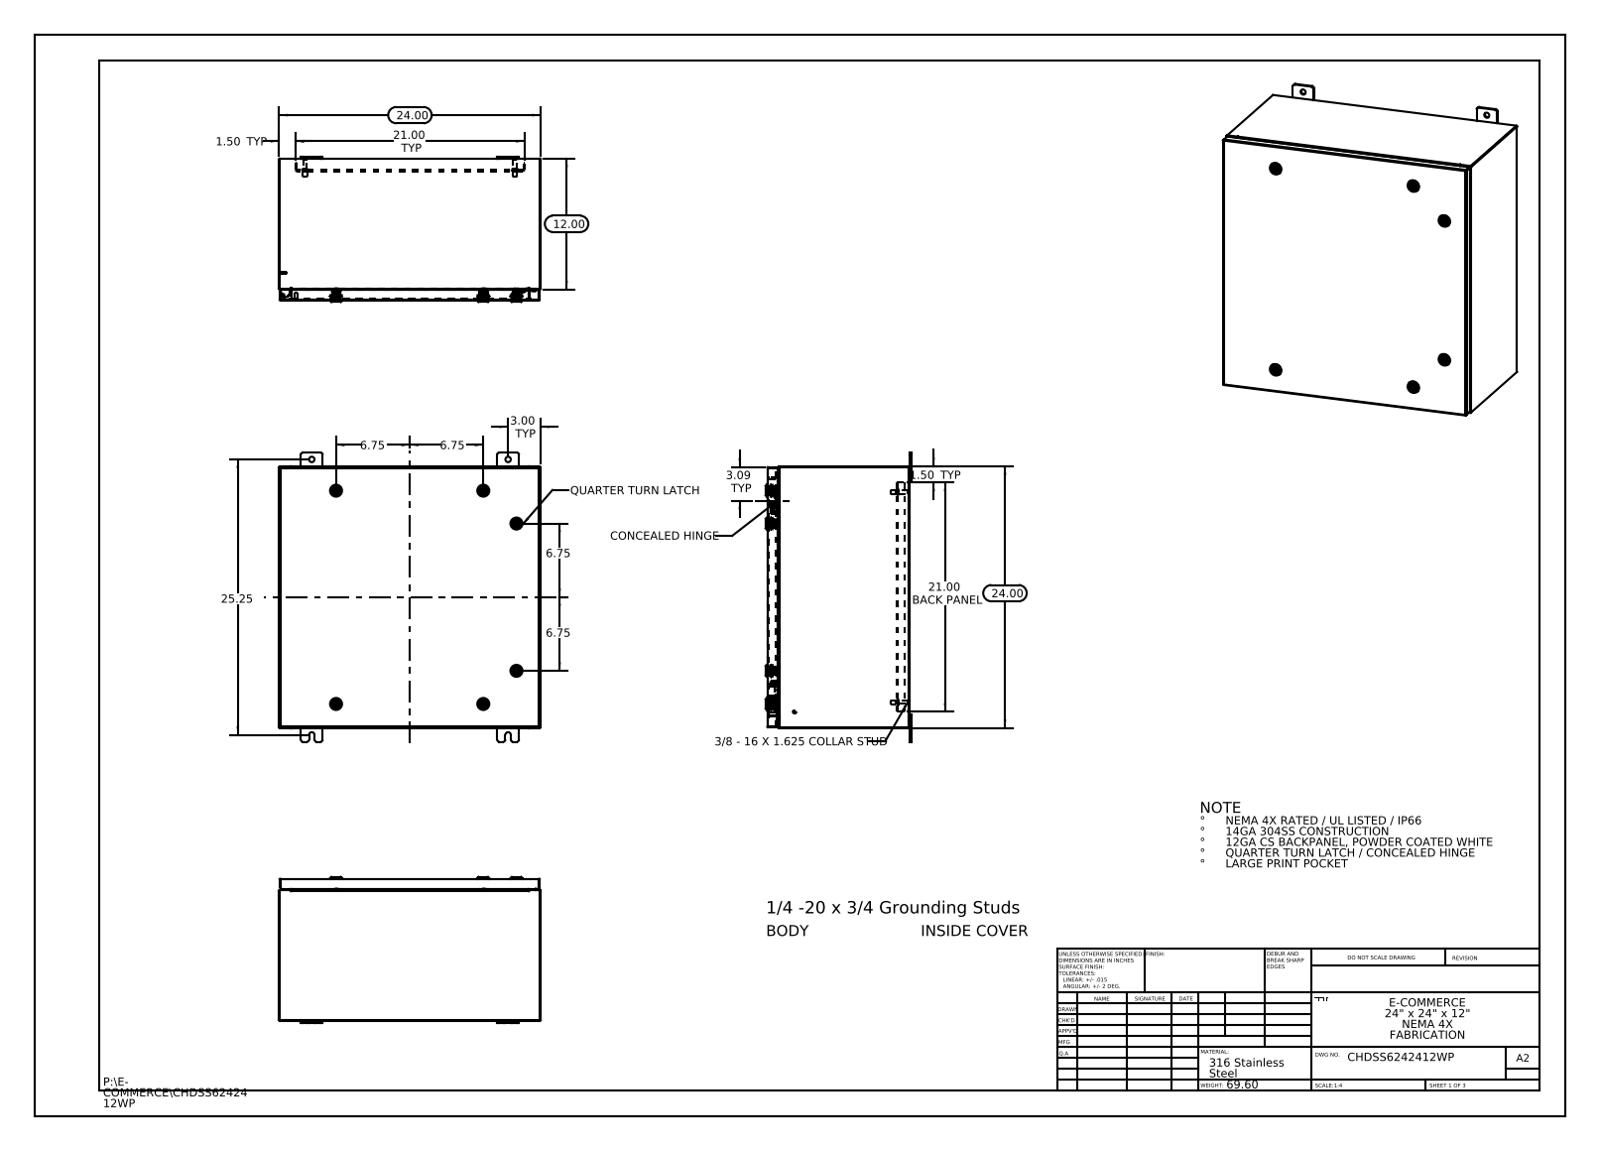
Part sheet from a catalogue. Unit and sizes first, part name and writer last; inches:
Units: inches
Overall size (bounding box): 26.5 × 24 × 13.356
Round holes (diameter × count): ⌀0.5 ×8, ⌀0.197 ×6, ⌀0.394 ×6, ⌀0.4 ×6, ⌀0.63 ×6, ⌀0.787 ×6, ⌀0.136 ×4, ⌀0.211 ×1
Round bosses / shafts (diameter × count): ⌀0.236 ×8, ⌀1.102 ×6, ⌀0.78 ×6, ⌀0.626 ×6, ⌀0.61 ×6, ⌀0.531 ×6, ⌀0.392 ×6, ⌀0.114 ×6
Partial cylindrical surfaces — rounded edges, fillets, slot ends (radius × count): R0.006 ×198, R0.118 ×198, R0.028 ×72, R0.02 ×24, R0.19 ×24, R0.197 ×24, R0.013 ×20, R0.088 ×18
Main face-to-face distances: 0.075, 23.925, 0.074, 23.85, 24, 13.01, 12.935, 12.936, 12.861, 0.104
Hole centre spacings: 13.5, 1.858, 2.878, 3.065, 16.376, 16.815, 18, 19.25
Volume: 247.1 in³ · Surface area: 6 219 in²
Bodies: 55 solids, 5420 faces (1592 planar, 1692 cylindrical, 2136 other)
Part name (STEP PRODUCT): HW-CLH-R001-0500_2412-026240-2445-Industrilas; CHDSS6242412WP Mounting Studs; CHDSS6242412WP Body; Concealed Hinge enclosure side (+8 more)
STEP written by: SolidWorks 2013 (CONFIG_CONTROL_DESIGN)
